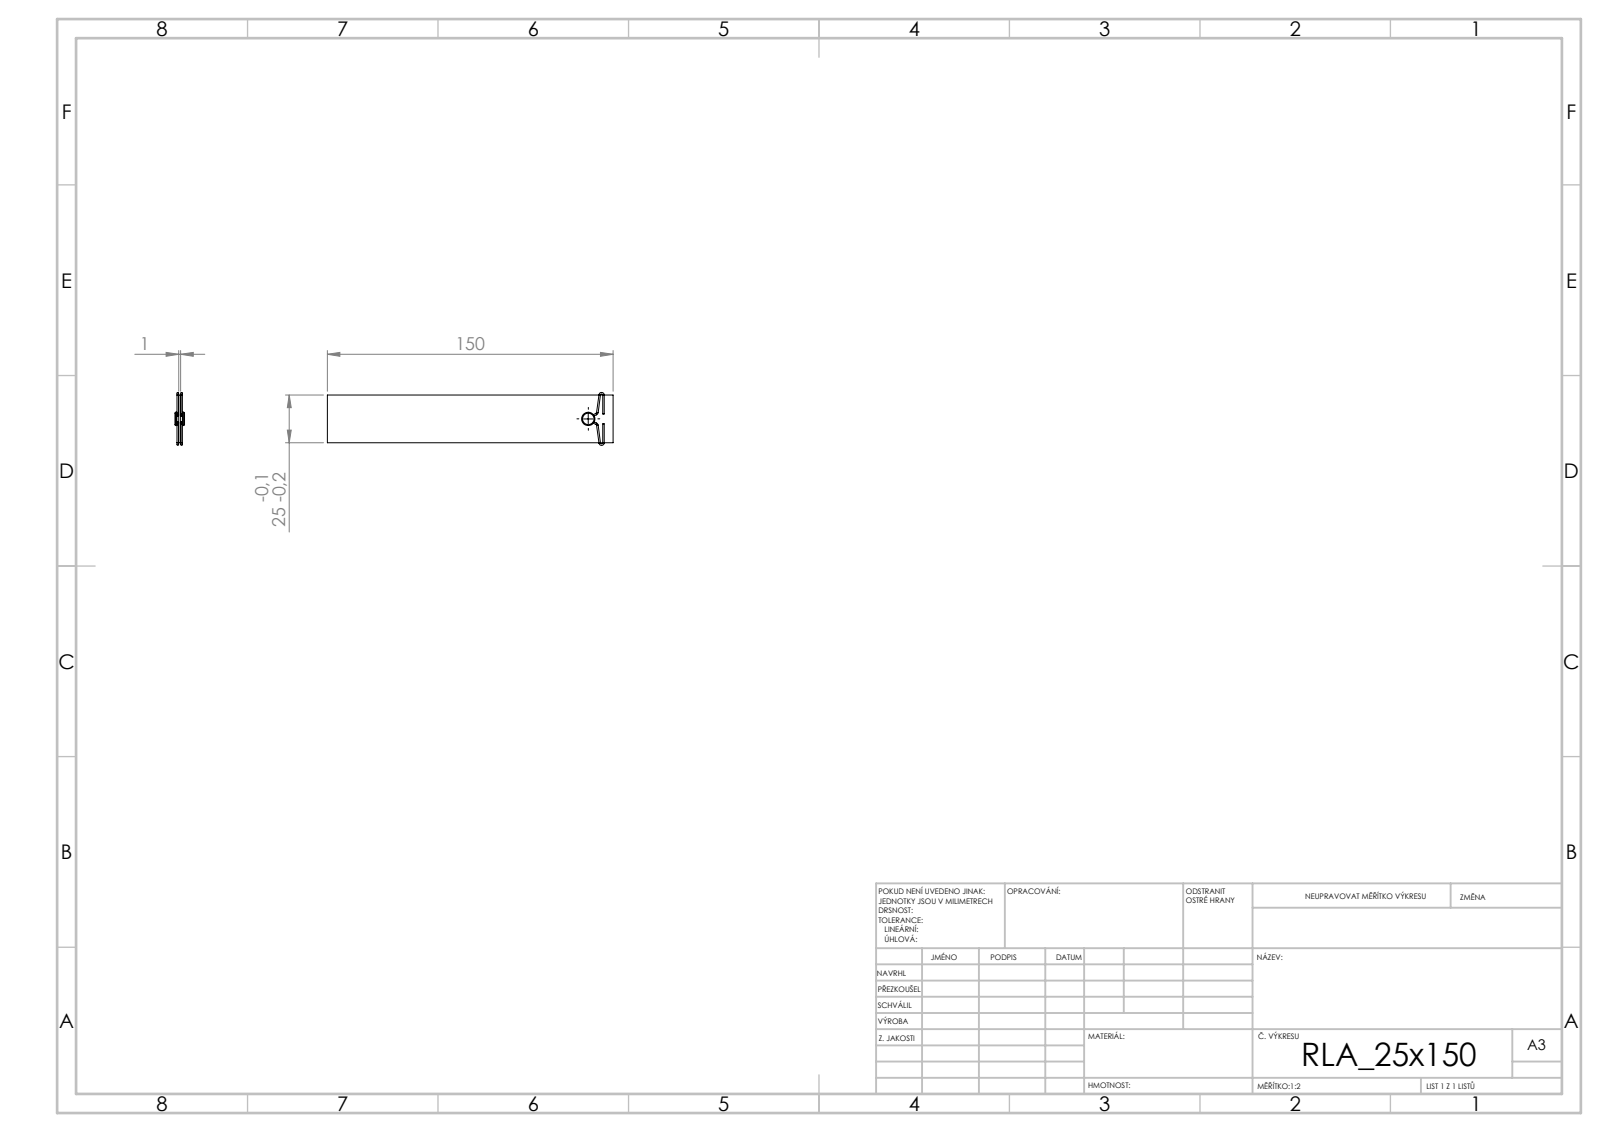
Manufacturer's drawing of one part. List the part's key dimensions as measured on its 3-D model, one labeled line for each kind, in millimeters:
STEP written by: SolidWorks 2019 (CONFIG_CONTROL_DESIGN)
Units: millimetres
Bodies: 3 solids, 82 faces (14 planar, 40 cylindrical, 28 other)
Overall size (bounding box): 150 × 27.8 × 5
Volume: 3 914 mm³ · Surface area: 8 335 mm²
Round bosses / shafts (diameter × count): ⌀0.8 ×14, ⌀7 ×1, ⌀4 ×1
Main face-to-face distances: 1, 25, 2, 3, 4, 5, 150, 9.95, 15.05, 5.1
